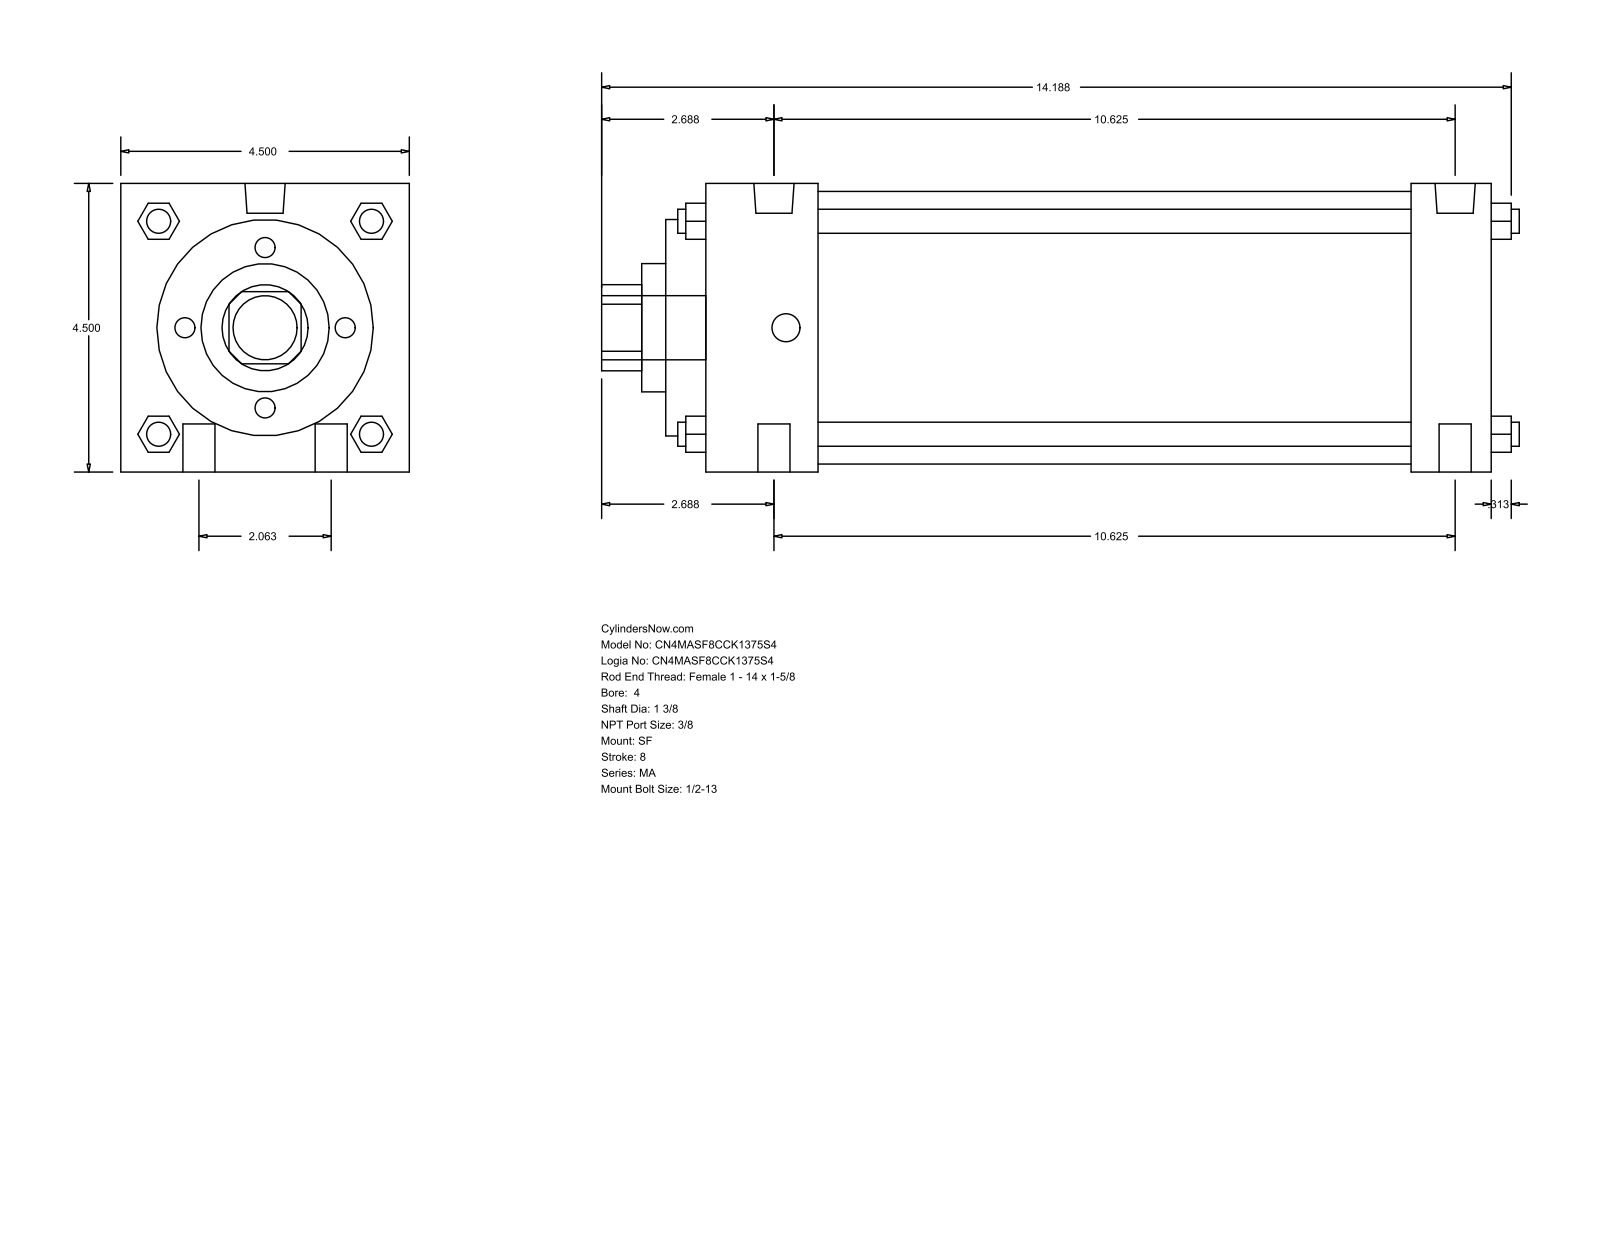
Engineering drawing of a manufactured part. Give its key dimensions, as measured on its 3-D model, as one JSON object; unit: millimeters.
{"part_name": "MA_SF__0400_1.375", "step_written_by": "GSSL Pune (CONFIG_CONTROL_DESIGN)", "units": "millimeters", "bodies": {"solids": 0, "faces": 126, "planar": 95, "cylindrical": 31, "other": 0}, "overall_size": [363.54, 114.3, 114.3], "round_holes": [[34.92, 1], [50.8, 1], [85.72, 1], [107.95, 1]], "round_bosses_or_shafts": [[12.7, 4], [9.53, 4], [15.93, 2], [11.11, 2], [25.4, 1]], "partial_cylinders_radius": [[17.06, 1]], "face_to_face_distances": [114.3, 311.16, 15.87, 327.03, 295.28, 279.41, 31.75, 60.32, 44.45, 234.96]}
